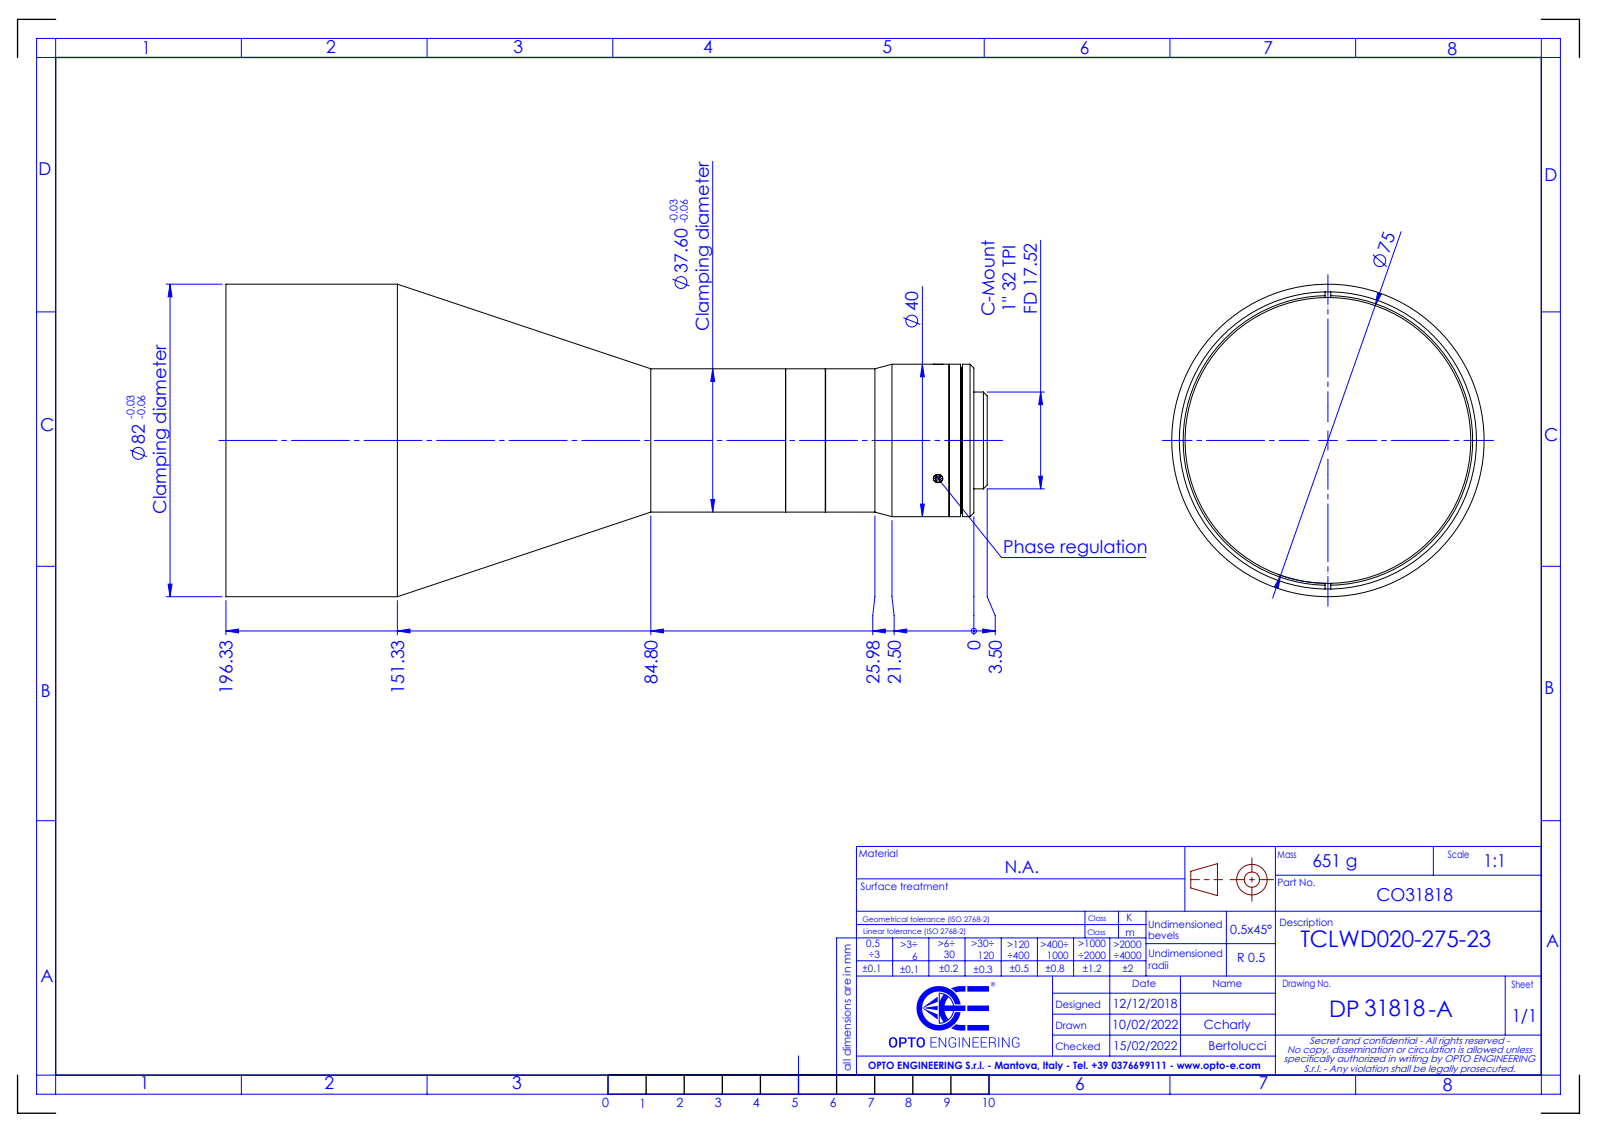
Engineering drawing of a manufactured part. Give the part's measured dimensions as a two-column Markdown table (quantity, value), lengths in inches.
| quantity | value |
| --- | --- |
| part name | DP31818-A_TCLWD020-275-23 |
| STEP written by | SolidWorks 2021 (CONFIG_CONTROL_DESIGN) |
| units | inches |
| bodies | 0 solids, 85 faces (38 planar, 28 cylindrical, 19 other) |
| overall size | 7.867 × 3.228 × 3.228 |
| round holes (diameter × count) | 0.098 × 2, 0.886 × 1, 1.004 × 1, 2.953 × 1, 3.071 × 1 |
| round bosses / shafts (diameter × count) | 3.228 × 1, 1.575 × 1, 1.48 × 1, 1 × 1 |
| main face-to-face distances | 0.138, 0.118, 0.02, 7.592, 7.611, 7.73, 0.256, 7.474, 6.198, 1.276 |
